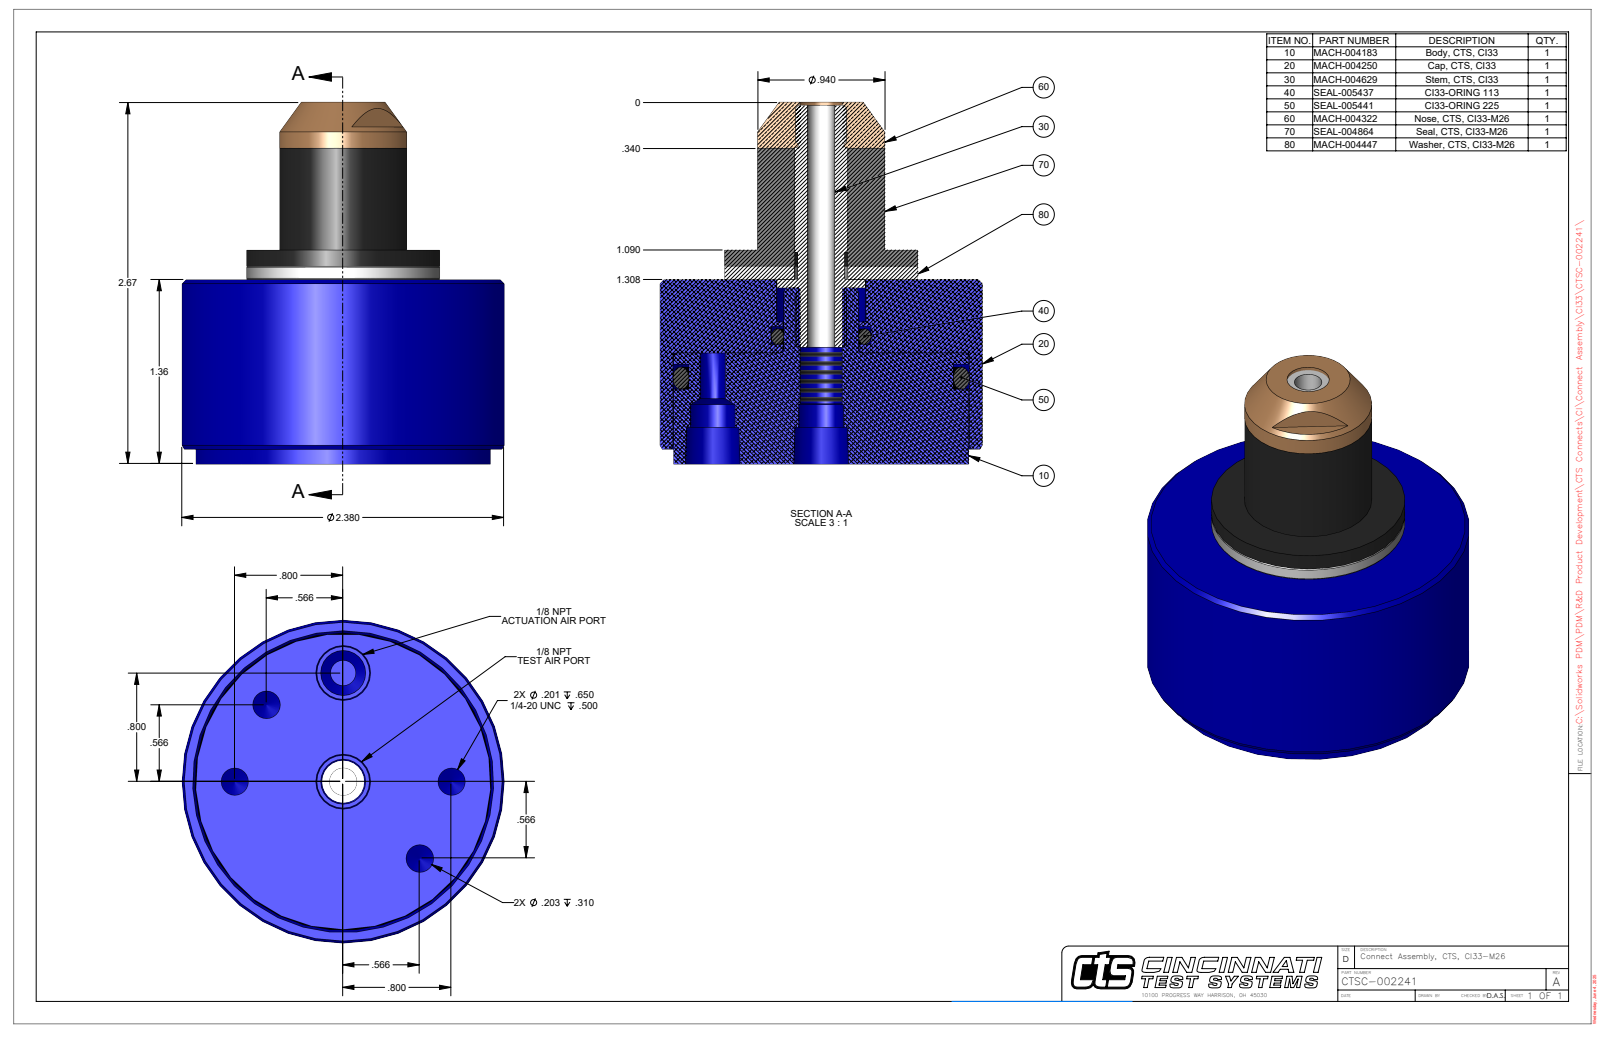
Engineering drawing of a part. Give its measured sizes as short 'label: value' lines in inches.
name: CTSC-002241
written by: SolidWorks 2023 (AUTOMOTIVE_DESIGN)
unit: in
bodies: 1 solid, 76 faces (20 planar, 32 cylindrical, 24 other)
size: 2.668 × 2.38 × 2.38
volume: 6.787 in³; area: 30.75 in²
holes: 2× ⌀0.201, 2× ⌀0.203, 2× ⌀0.332, 1× ⌀0.203, 1× ⌀0.313, 1× ⌀0.659, 1× ⌀2.188
bosses: 1× ⌀2.38, 1× ⌀2.178, 1× ⌀1.427, 1× ⌀0.94, 1× ⌀0.65
face distances: 1.36, 1.578, 0.218, 0.11, 1.25, 1.468, 2.668, 2.558, 1.308, 1.09
hole spacings: 0.8, 0.612, 1.478, 1.131, 1.6
